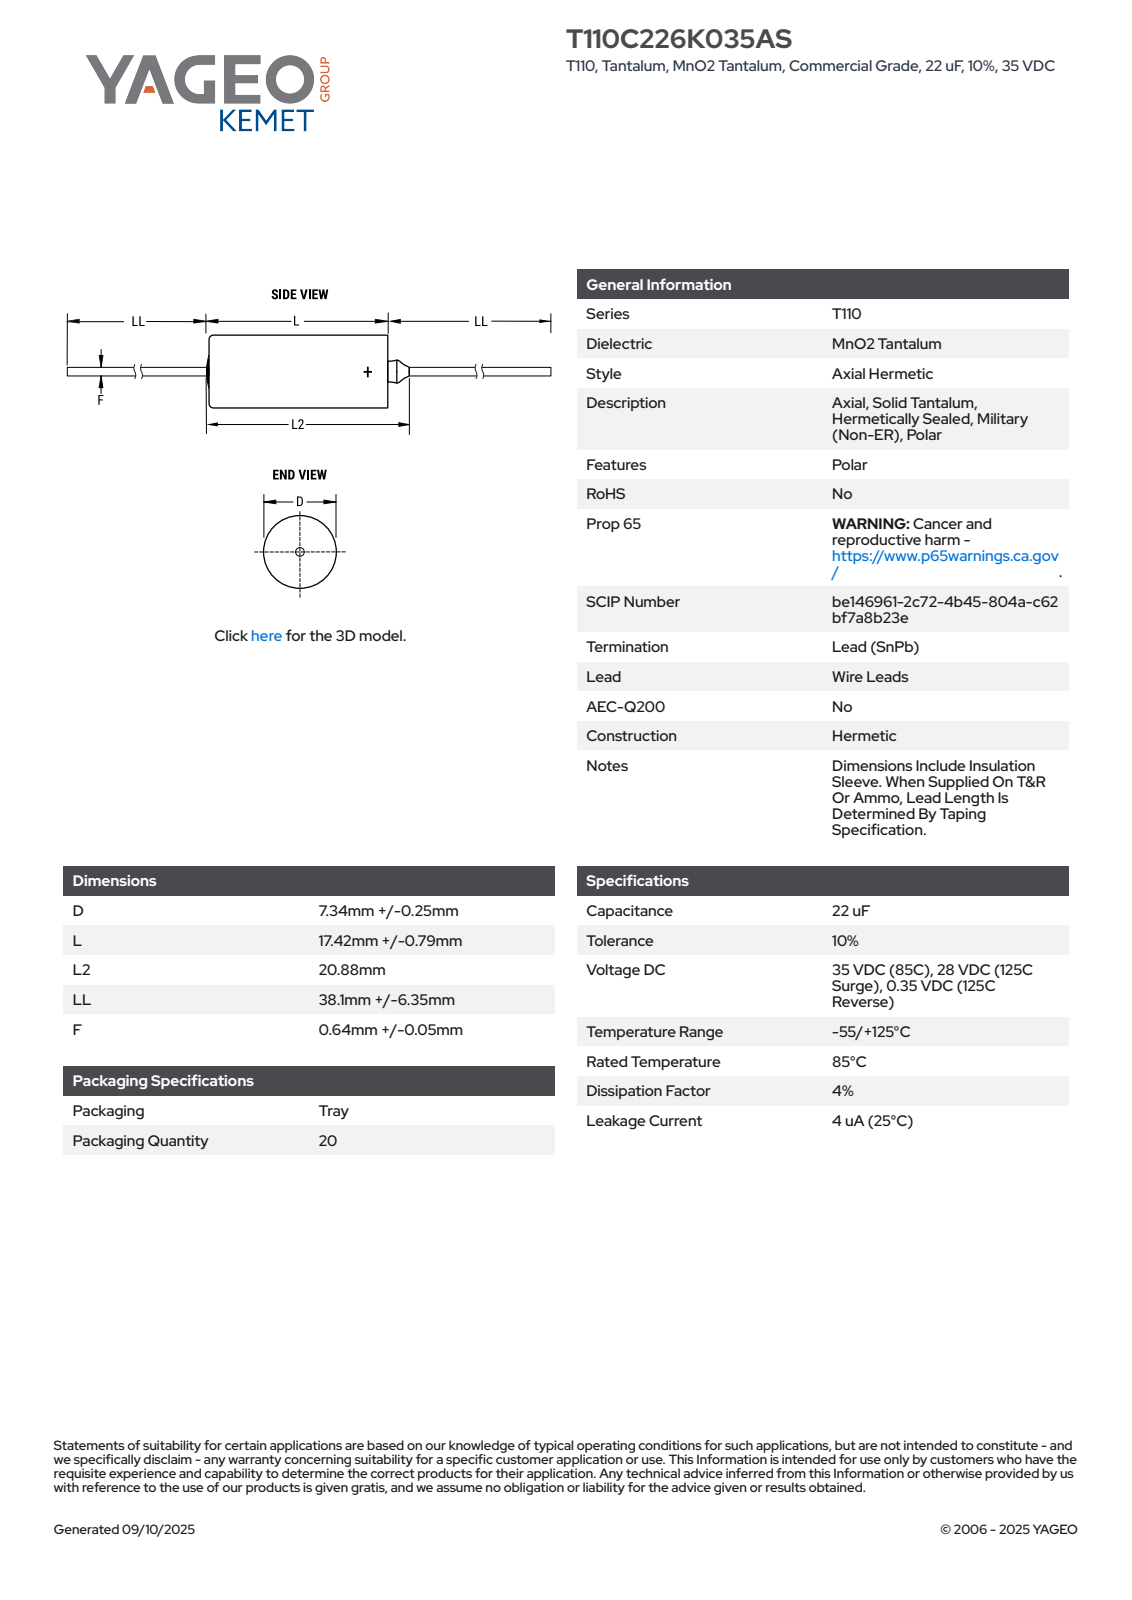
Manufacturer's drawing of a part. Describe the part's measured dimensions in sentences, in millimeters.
The part is named "CTAM_C_D7.59L18.21L220.88LL44.45F0.69". Its 3-D file was written by "SolidWorks 2014 (AUTOMOTIVE_DESIGN)". It is 1 solid with 98 faces: 29 planar, 30 cylindrical and 39 other. Overall it measures 107.11 by 7.59 by 7.59 millimeters. Its volume is 674 cubic millimeters and its surface area 836 square millimeters. Round holes: 1 of diameter 7.19. Round bosses or shafts: 1 of diameter 7.59, 1 of diameter 1.33, 1 of diameter 1.3, 1 of diameter 0.69. Partial cylindrical surfaces (rounded edges, fillets, slot ends): 1 of radius 3.79. The main face-to-face distances are 13.52, 18.04, 4.52, 44.62, 58.14, 62.66, 107.11, 62.49, 48.97, 44.45.
